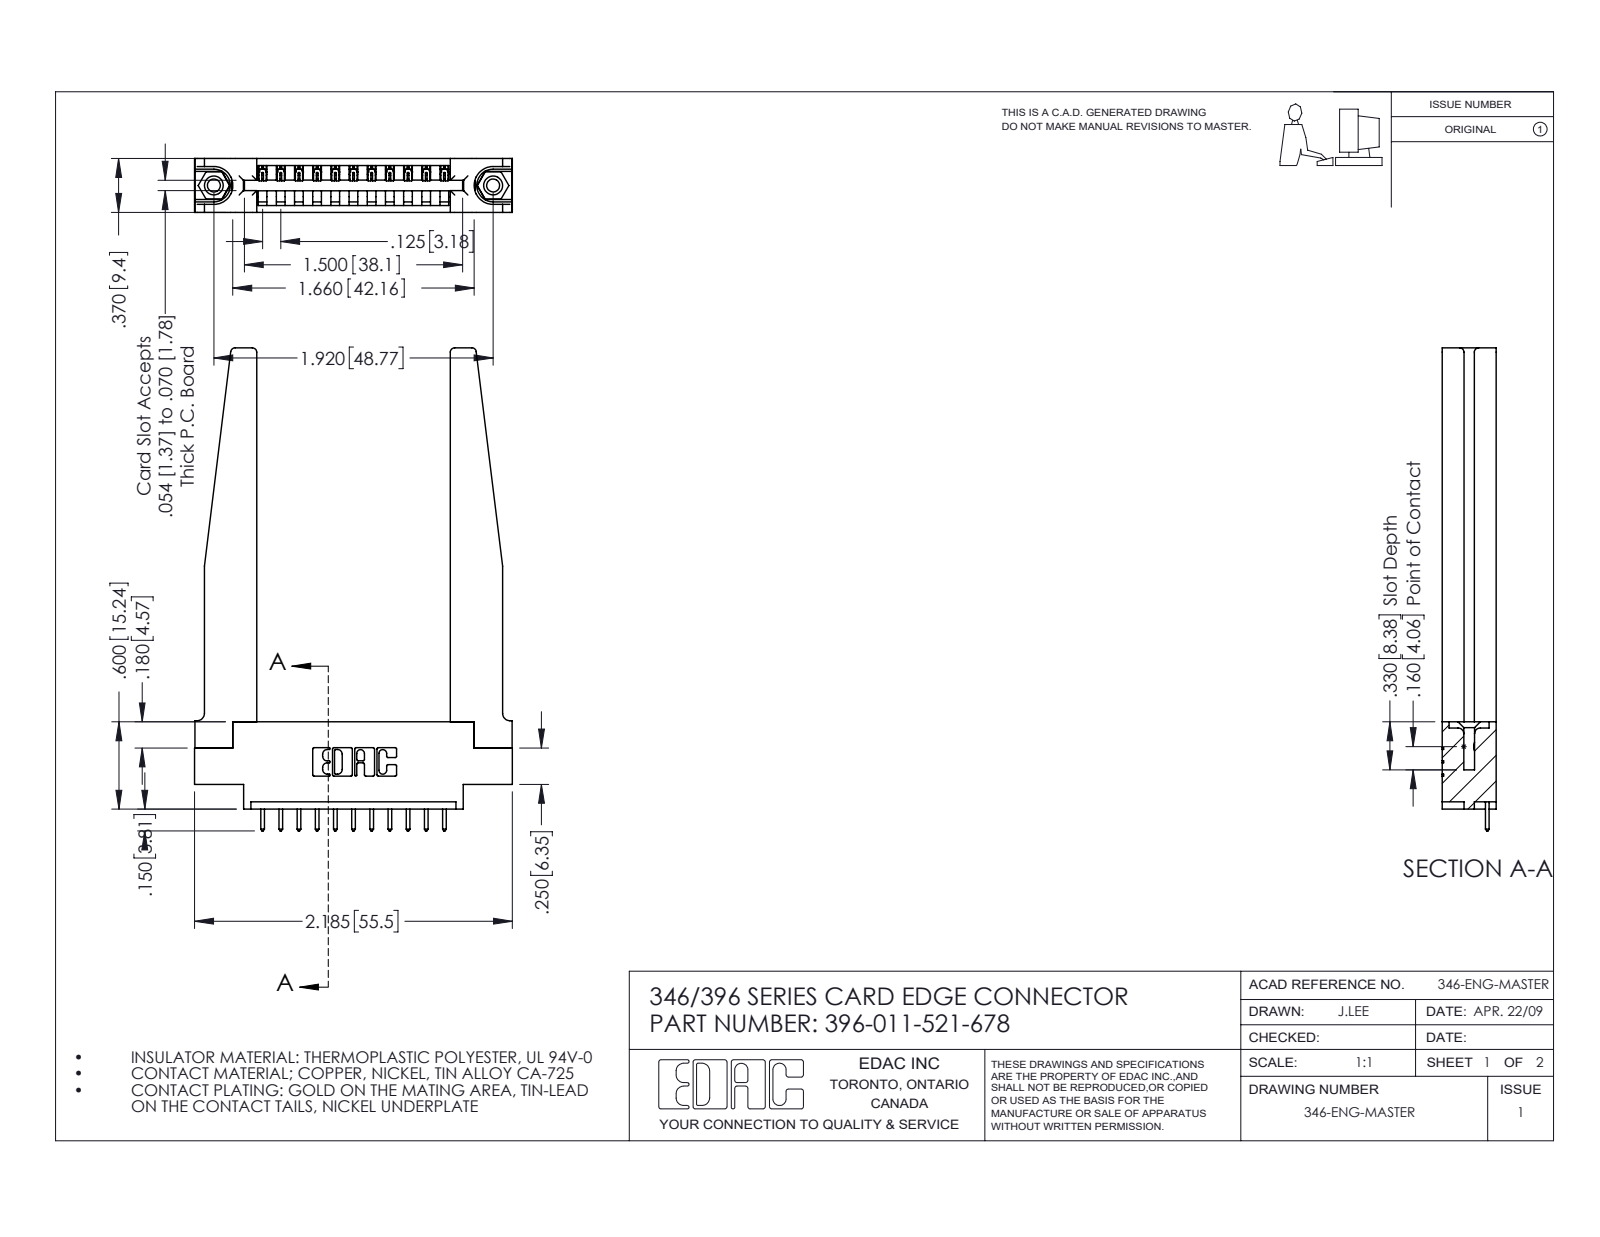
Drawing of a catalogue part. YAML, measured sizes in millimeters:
part_name: "345-292-001_345-293-121; 396-011-521-678; 345-250-001_345-250-001-102; 346-220-078_345-220-078 (+1 more)"
step_written_by: "SolidWorks 2016 (CONFIG_CONTROL_DESIGN)"
units: millimeters
bodies: {solids: 16, faces: 998, planar: 662, cylindrical: 284, other: 52}
overall_size: [84.3, 55.5, 9.4]
volume: 11800
surface_area: 12380
round_holes:
  - {diameter: 2.3, count: 2}
  - {diameter: 3.2, count: 2}
  - {diameter: 4, count: 2}
  - {diameter: 1.6, count: 1}
round_bosses_or_shafts:
  - {diameter: 3.9, count: 2}
partial_cylinders:
  - {radius: 0.2, count: 22}
  - {radius: 0.3, count: 22}
  - {radius: 0.3, count: 22}
  - {radius: 0.8, count: 8}
  - {radius: 0.2, count: 6}
  - {radius: 0.8, count: 6}
  - {radius: 0.7, count: 3}
  - {radius: 0.8, count: 2}
face_to_face_distances: [9.4, 3.8, 1.8, 3.8, 1.2, 8.2, 5.6, 6.4, 2.6, 4.4]
hole_center_spacings: [6.2, 43.6, 48.8]
